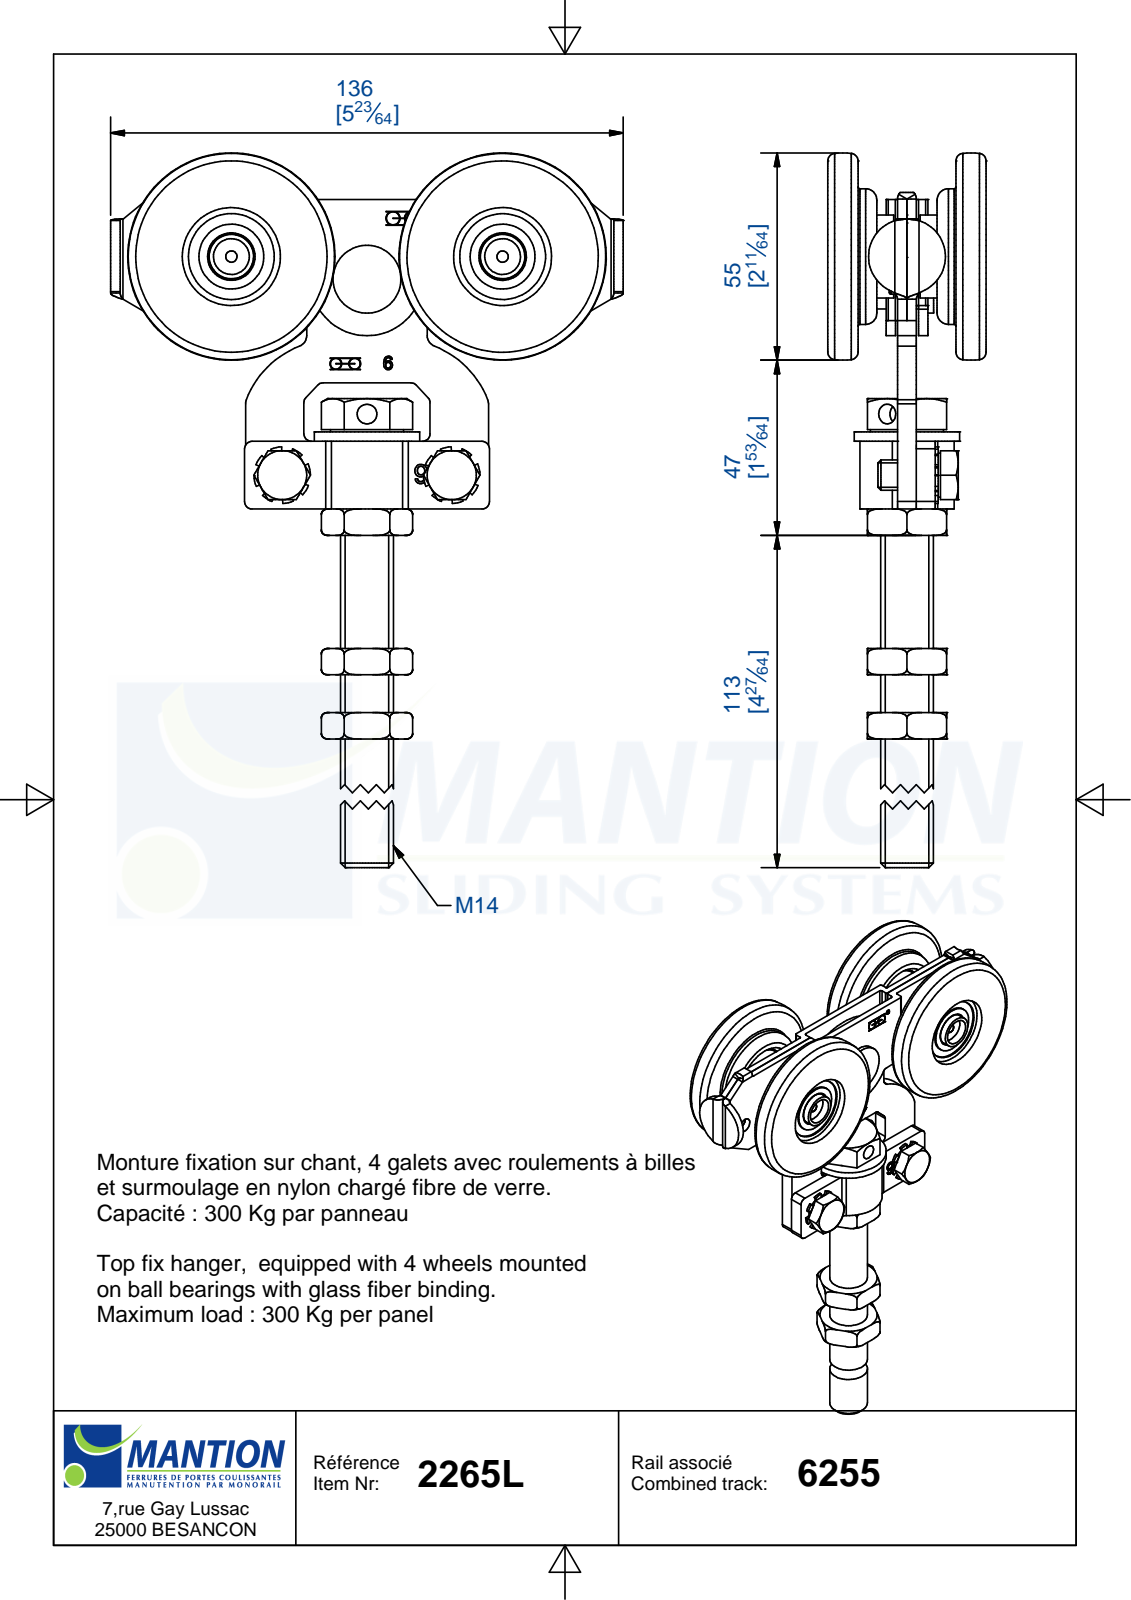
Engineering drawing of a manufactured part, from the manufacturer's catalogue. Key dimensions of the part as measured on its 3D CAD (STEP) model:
Part name (STEP PRODUCT): Pi\S\hce2
STEP written by: Autodesk Inventor 2011 (AUTOMOTIVE_DESIGN)
Units: millimetres
Bodies: 4 solids, 665 faces (243 planar, 171 cylindrical, 251 other)
Overall size (bounding box): 213.69 × 136 × 42
Volume: 170 160 mm³ · Surface area: 77 451 mm²
Round holes (diameter × count): ⌀5.1 ×3, ⌀3 ×2, ⌀6.65 ×2, ⌀9 ×2, ⌀9.5 ×2, ⌀12 ×2, ⌀12.2 ×2, ⌀22.78 ×2, ⌀26 ×2, ⌀28 ×2, ⌀14.2 ×1, ⌀16.2 ×1
Round bosses / shafts (diameter × count): ⌀22 ×2, ⌀17.22 ×2, ⌀11.8 ×2, ⌀8 ×2, ⌀2.9 ×2, ⌀28 ×1, ⌀19.37 ×1, ⌀18 ×1
Partial cylindrical surfaces — rounded edges, fillets, slot ends (radius × count): R1 ×32, R2 ×12, R3 ×8, R25 ×3, R1.55 ×2, R4 ×2, R7 ×2, R9.69 ×2
Main face-to-face distances: 18.5, 8, 5, 23.5, 10.5, 2.5, 15.5, 13, 5.5, 26.5
Hole centre spacings: 36.45, 56.66, 59.25, 82.16, 45, 72
